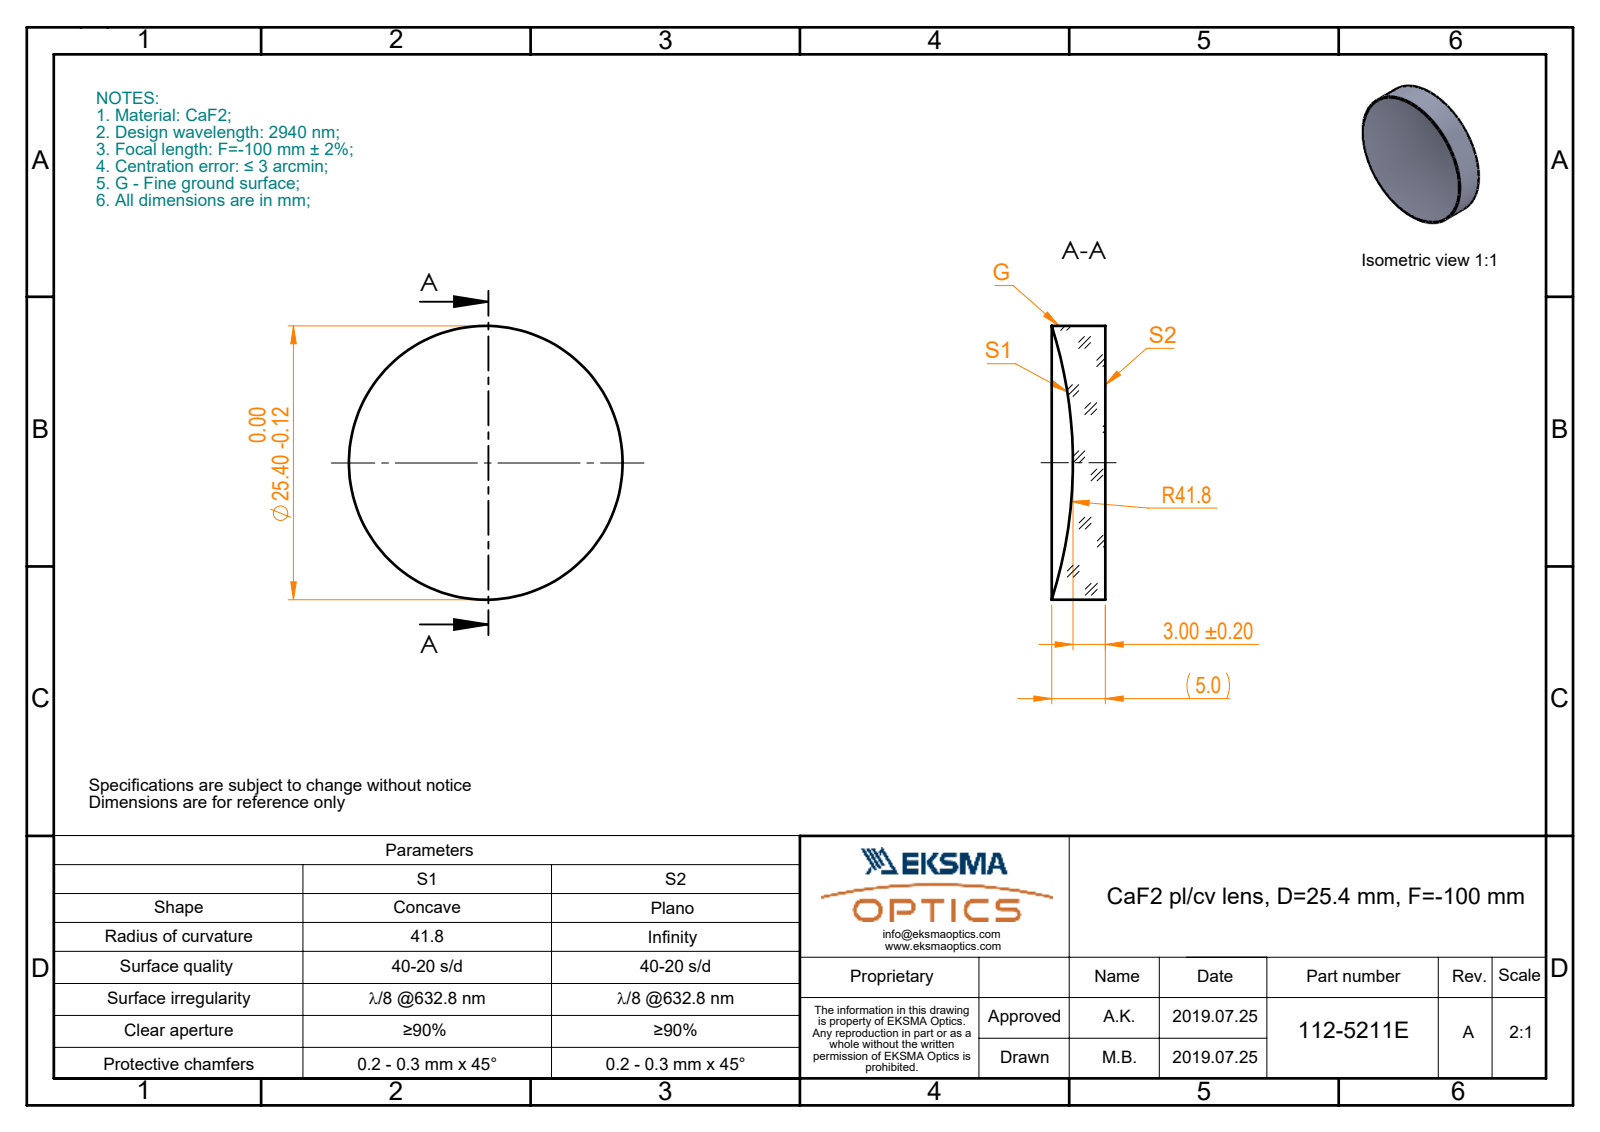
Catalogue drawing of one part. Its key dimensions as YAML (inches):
part_name: "112-5211E CaF2 pl-cv 12.7 F-100"
step_written_by: "SolidWorks 2017 (CONFIG_CONTROL_DESIGN)"
units: inches
bodies: {solids: 1, faces: 5, planar: 1, cylindrical: 2, other: 2}
overall_size: [1, 1, 0.196]
volume: 0.123
surface_area: 2.206
round_bosses_or_shafts:
  - {diameter: 1, count: 1}
